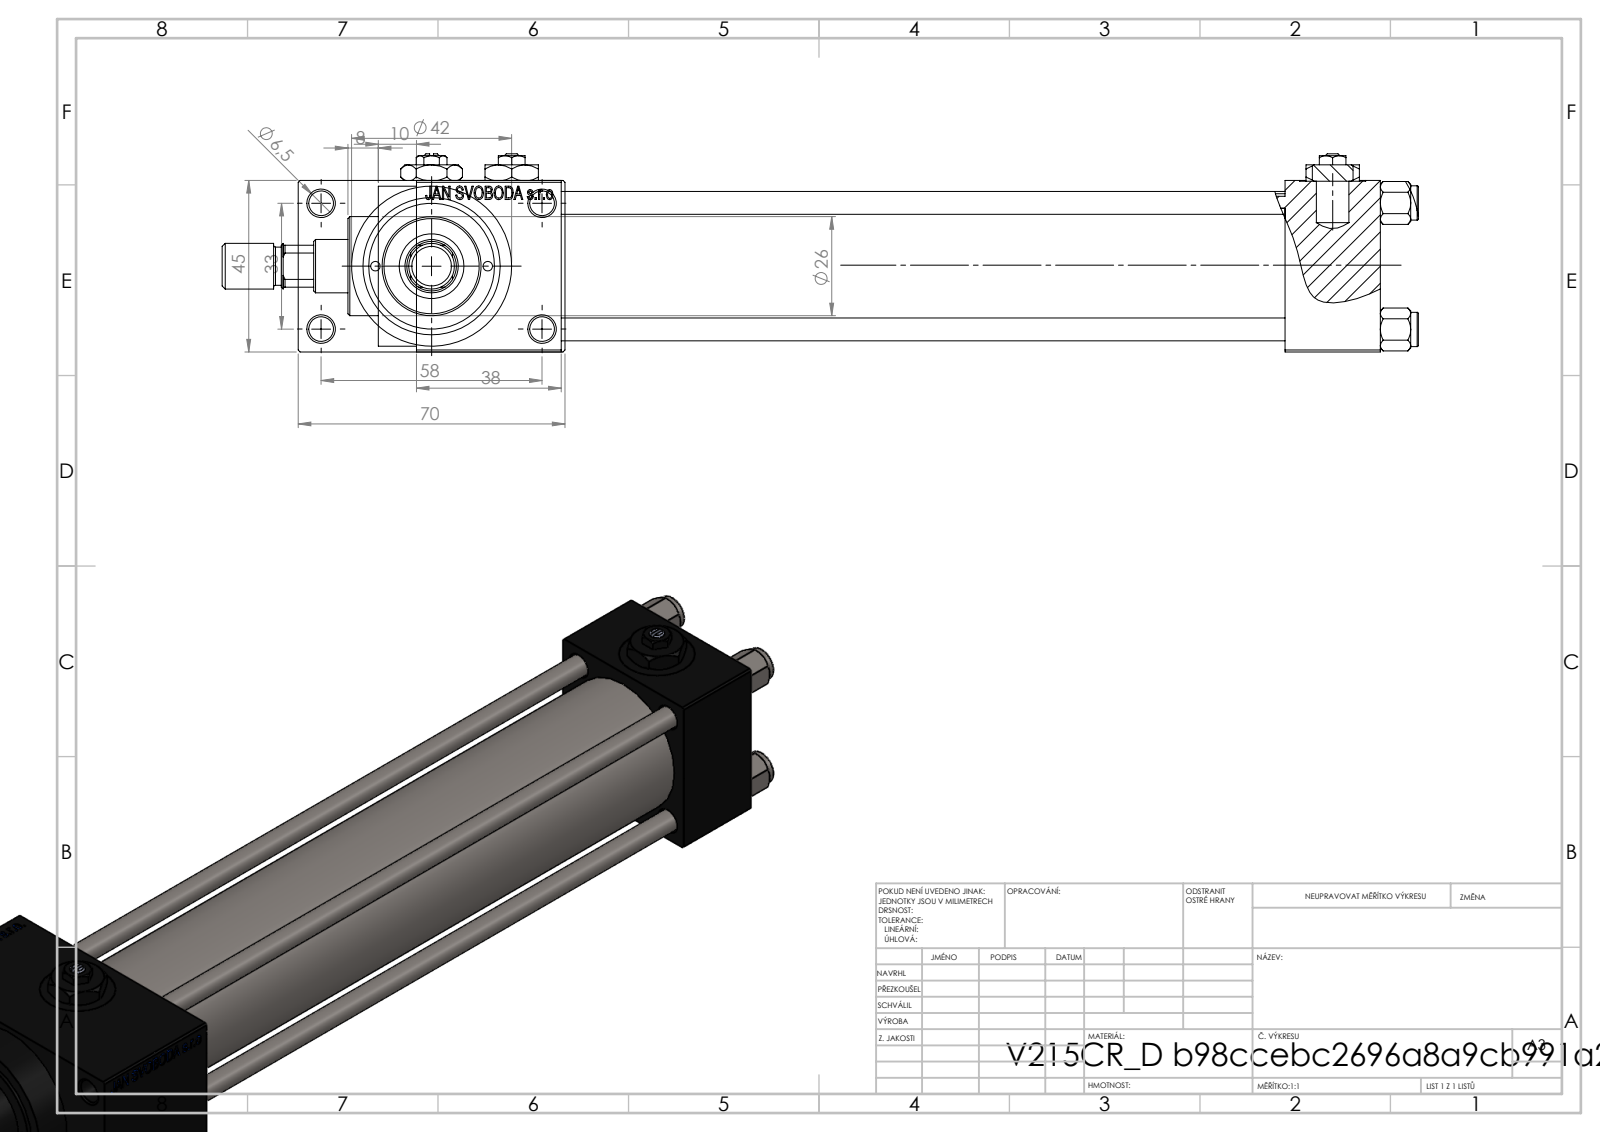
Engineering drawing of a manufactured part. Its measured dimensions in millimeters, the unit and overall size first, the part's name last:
Units: millimetres
Overall size (bounding box): 314 × 70 × 52
Round holes (diameter × count): ⌀6.5 ×5, ⌀6 ×4, ⌀13.16 ×4, ⌀20 ×4, ⌀7 ×3, ⌀2.5 ×2, ⌀14 ×1, ⌀17 ×1, ⌀24 ×1, ⌀32 ×1, ⌀33 ×1
Round bosses / shafts (diameter × count): ⌀9 ×4, ⌀42 ×1, ⌀38 ×1, ⌀26 ×1, ⌀12 ×1, ⌀10 ×1
Partial cylindrical surfaces — rounded edges, fillets, slot ends (radius × count): R6.5 ×1
Main face-to-face distances: 45, 25, 12.5, 190, 215, 57.5, 228, 38, 253, 70
Hole centre spacings: 12.4, 16.7, 21.8, 23.48, 33.2, 33.37, 35.35, 35.47
Volume: 314 198 mm³ · Surface area: 125 469 mm²
Bodies: 14 solids, 1223 faces (548 planar, 107 cylindrical, 568 other)
Part name (STEP PRODUCT): Zatka_pro_OIL_PORT; V215CR_VCP_D; V215_VC_A; NUT_M5_D (+3 more)
STEP written by: SolidWorks 2019 (CONFIG_CONTROL_DESIGN)
